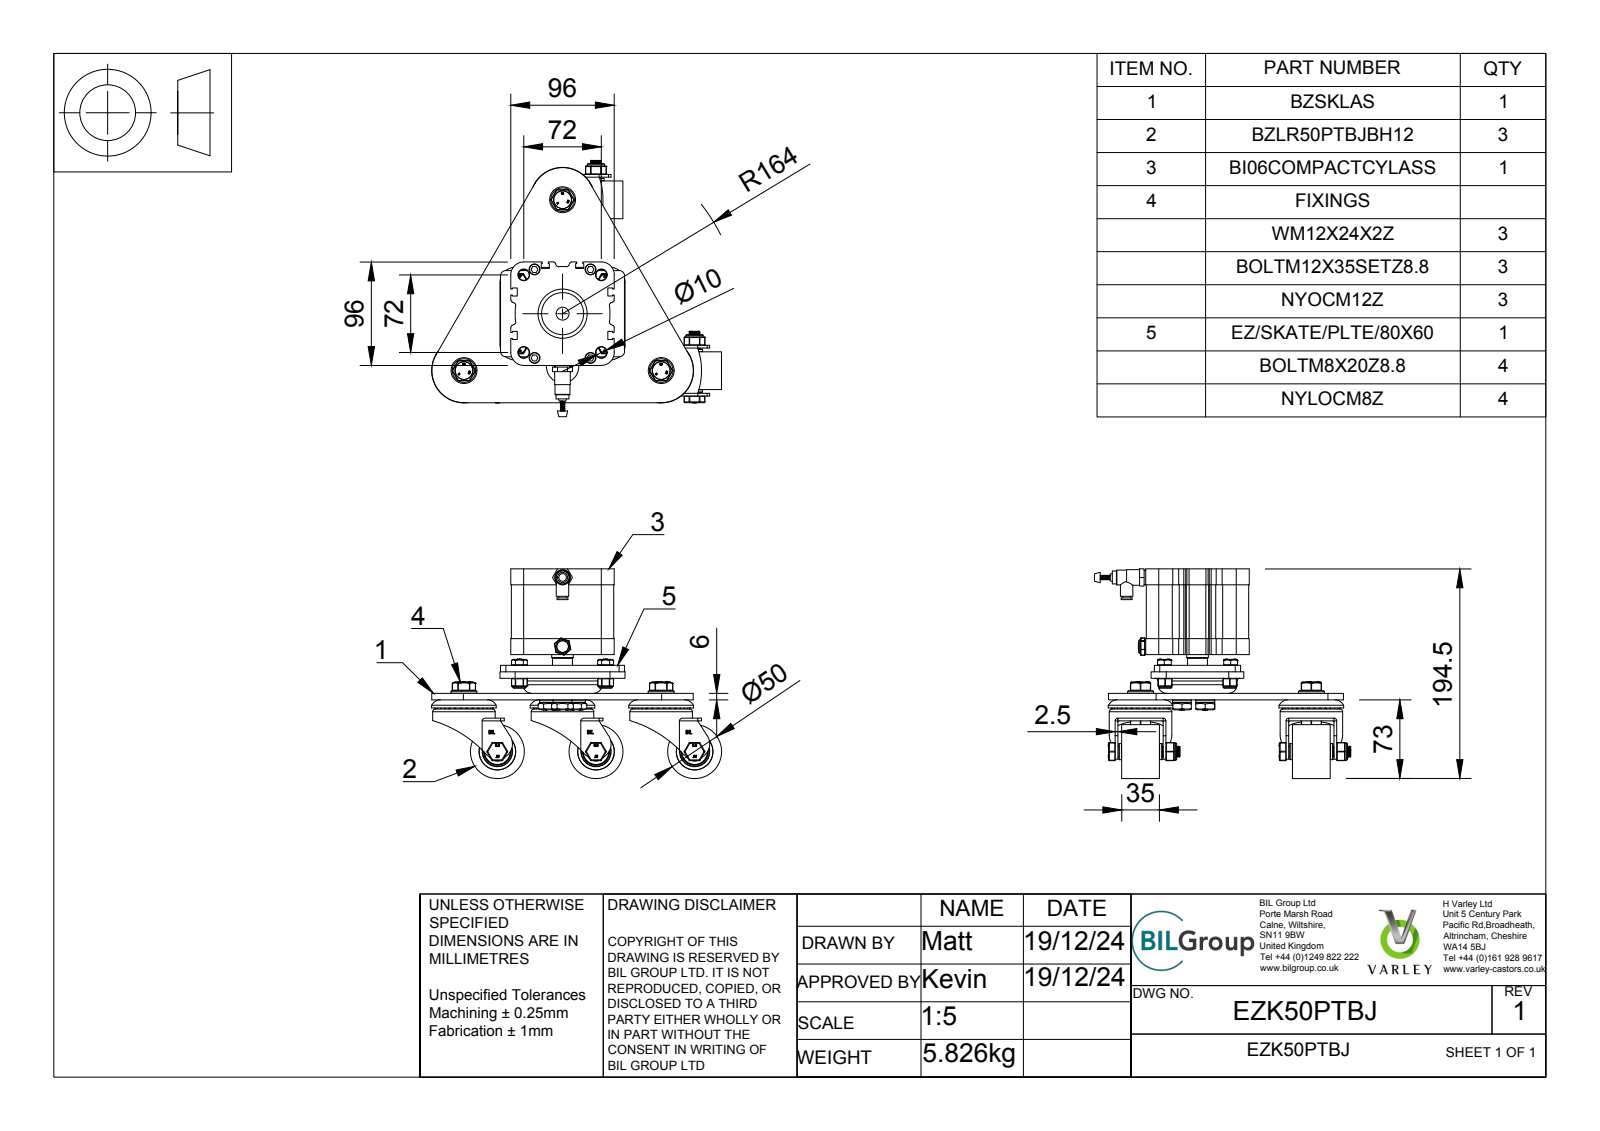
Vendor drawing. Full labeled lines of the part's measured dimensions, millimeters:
Part name (STEP PRODUCT): EZK50PTBJ v4; BZSKLAS v1; SCENERY SKATE; TRIANGLE (+7 more)
STEP written by: Autodesk Translation Framework v13.20.0.188 (AP242_MANAGED_MODEL_BASED_3D_ENGINEERING_MIM_LF)
Units: millimetres
Bodies: 243 solids, 4543 faces (1528 planar, 1509 cylindrical, 1506 other)
Overall size (bounding box): 269 × 237.66 × 194.5
Volume: 1 322 000 mm³ · Surface area: 490 235 mm²
Round holes (diameter × count): ⌀10 ×14, ⌀8 ×9, ⌀12 ×7, ⌀0.8 ×6, ⌀11 ×5, ⌀8.6 ×4, ⌀10.2 ×3, ⌀10.5 ×3, ⌀12.2 ×3, ⌀12.5 ×3, ⌀13 ×3, ⌀14 ×3
Round bosses / shafts (diameter × count): ⌀28 ×6, ⌀13 ×5, ⌀12 ×5, ⌀18.5 ×4, ⌀12.1 ×4, ⌀9.5 ×4, ⌀7.87 ×4, ⌀6.45 ×4
Partial cylindrical surfaces — rounded edges, fillets, slot ends (radius × count): R0.5 ×170, R0.25 ×38, R0.75 ×34, R1 ×18, R0.27 ×16, R0.51 ×16, R0.4 ×12, R0.77 ×12
Main face-to-face distances: 6, 26, 20, 50.75, 106.75, 100.75, 56.75, 50, 14.75, 64.75
Hole centre spacings: 25, 99.23, 7.21, 11.18, 17.8, 31.05, 37.95, 46.53
